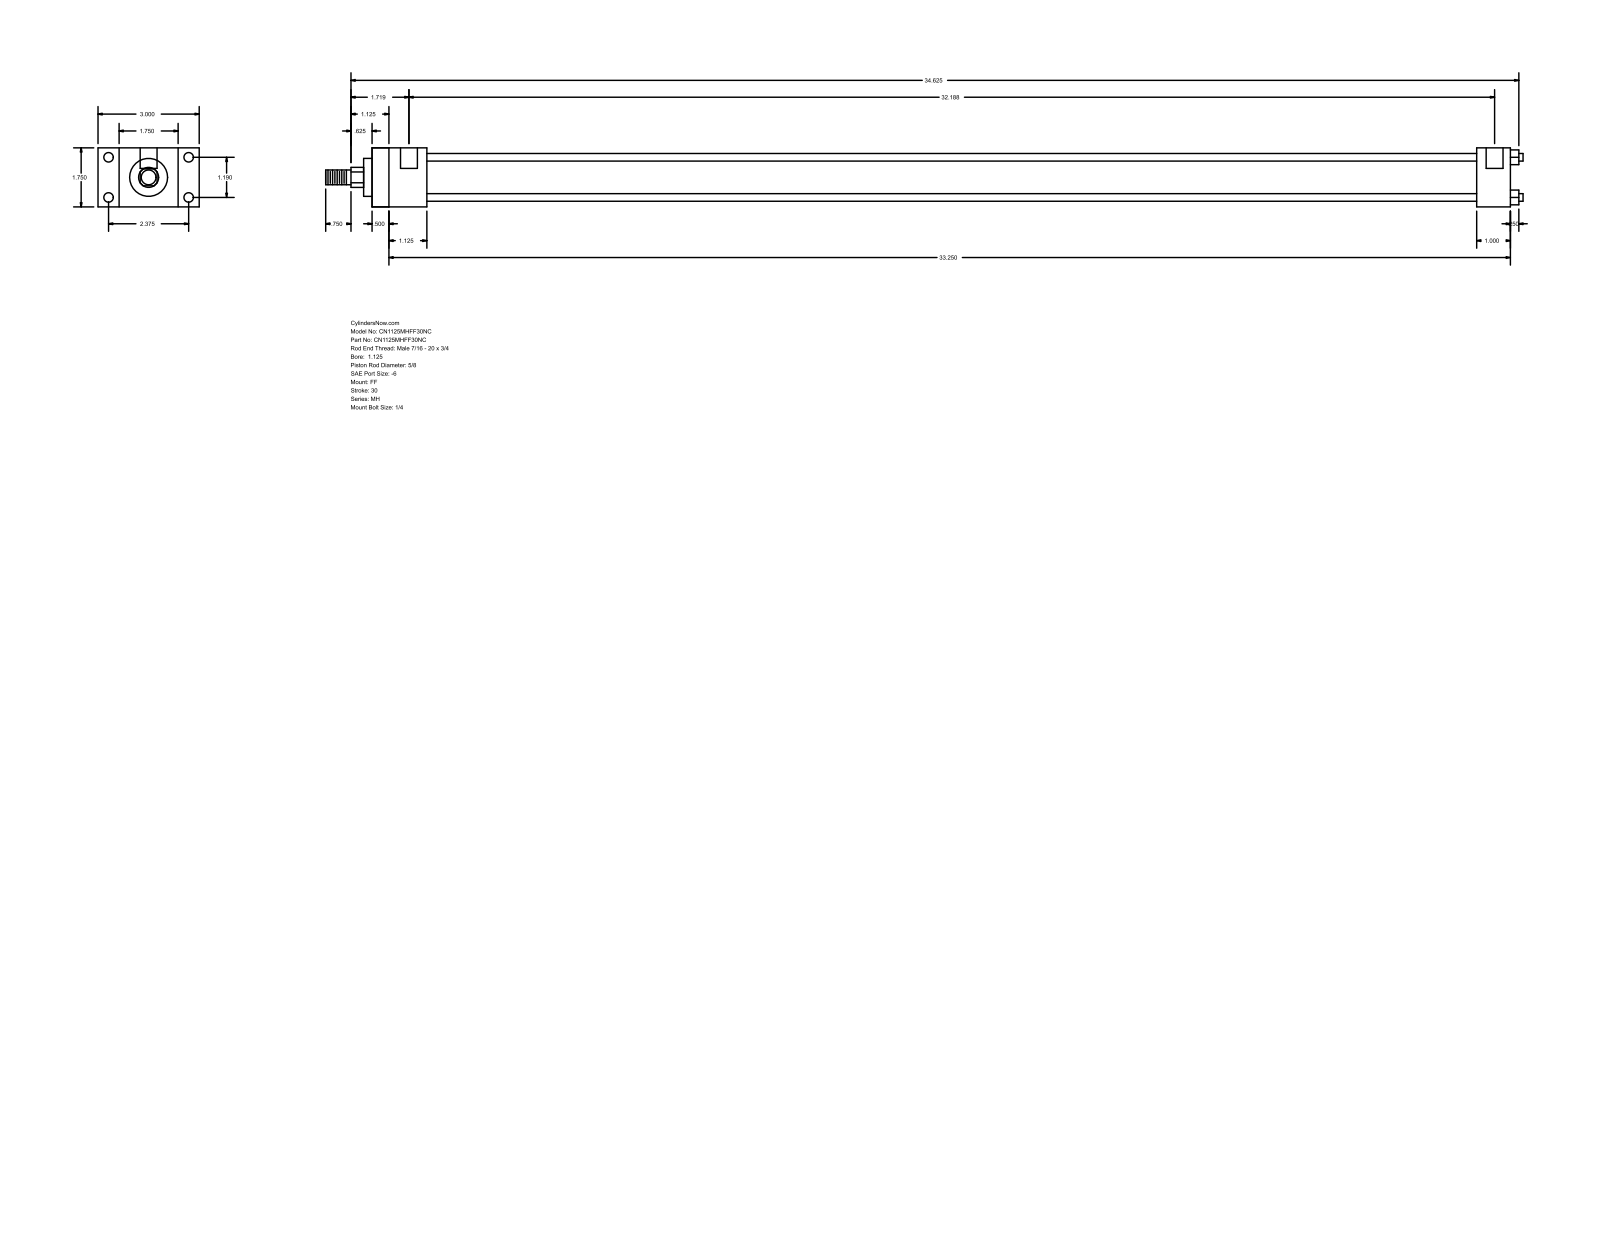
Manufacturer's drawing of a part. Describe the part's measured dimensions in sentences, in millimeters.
The part is named "MH_FF__0112_0.625". Its 3-D file was written by "GSSL Pune (CONFIG_CONTROL_DESIGN)". It is 0 solids with 92 faces: 64 planar, 28 cylindrical and 0 other. Overall it measures 901.7 by 76.2 by 44.45 millimeters. Round holes: 4 of diameter 5.56, 4 of diameter 7.14, 2 of diameter 12.7. Round bosses or shafts: 4 of diameter 5.71, 1 of diameter 34.92, 1 of diameter 28.57, 1 of diameter 15.88, 1 of diameter 11.11. Partial cylindrical surfaces (rounded edges, fillets, slot ends): 1 of radius 7.54. The main face-to-face distances are 44.46, 857.24, 15.87, 12.69, 844.55, 28.58, 60.33, 41.27, 831.85, 819.16. The hole center spacings are 30.22, 60.32, 67.47, 814.39, 3.17, 817.56.
